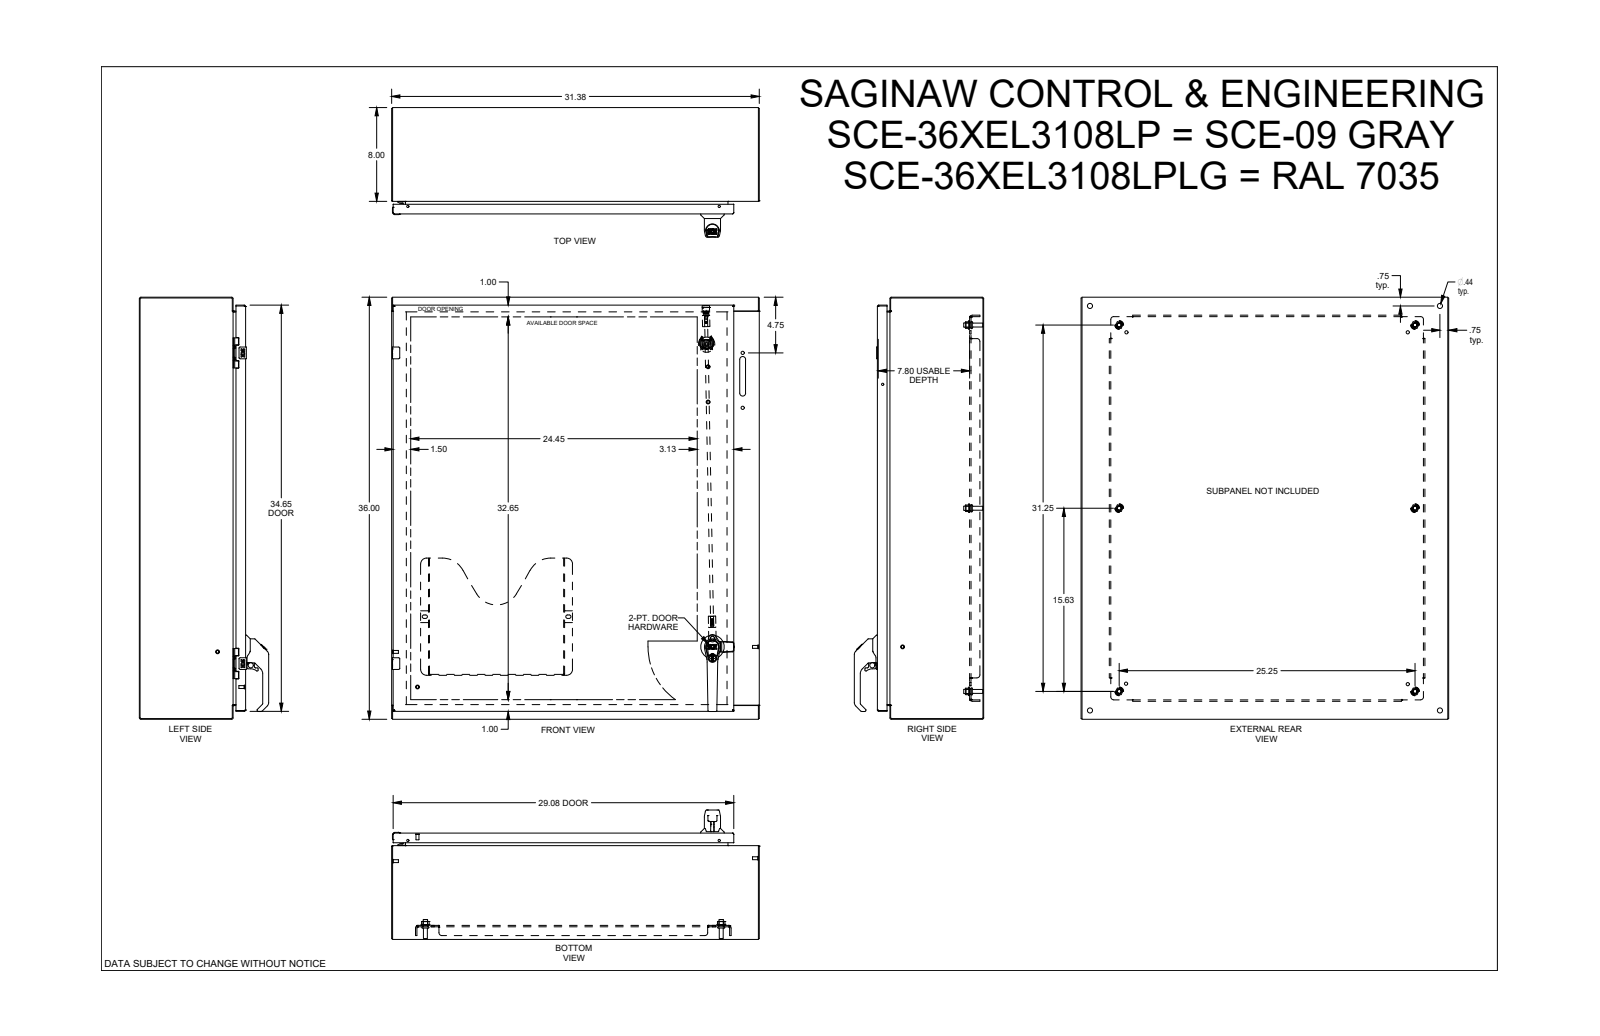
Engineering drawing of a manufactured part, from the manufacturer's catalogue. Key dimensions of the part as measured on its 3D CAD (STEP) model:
Part name (STEP PRODUCT): SCE-36XEL3108LPLG
STEP written by: SolidWorks 2019 (CONFIG_CONTROL_DESIGN)
Units: inches
Bodies: 0 solids, 4750 faces (1773 planar, 1244 cylindrical, 1733 other)
Overall size (bounding box): 36 × 31.375 × 11.041
Round holes (diameter × count): ⌀0.281 ×6, ⌀0.367 ×6, ⌀0.5 ×6, ⌀0.266 ×5, ⌀0.172 ×4, ⌀0.205 ×4, ⌀0.244 ×4, ⌀0.375 ×4, ⌀0.437 ×4, ⌀0.25 ×3, ⌀0.04 ×2, ⌀0.138 ×2
Round bosses / shafts (diameter × count): ⌀0.248 ×8, ⌀0.366 ×6, ⌀0.332 ×6, ⌀0.17 ×6, ⌀0.25 ×5, ⌀0.24 ×4, ⌀0.563 ×3, ⌀0.196 ×3
Partial cylindrical surfaces — rounded edges, fillets, slot ends (radius × count): R0.03 ×71, R0.015 ×50, R0.01 ×44, R0.02 ×43, R0.02 ×36, R0.039 ×30, R0.005 ×26, R0.04 ×25
Main face-to-face distances: 0.075, 0.075, 8.998, 8.923, 9.073, 8.998, 1.2, 7.873, 0.125, 7.923
Hole centre spacings: 26.5, 0.985, 0.493, 0.02, 0.494, 4.493, 0.472, 0.725
